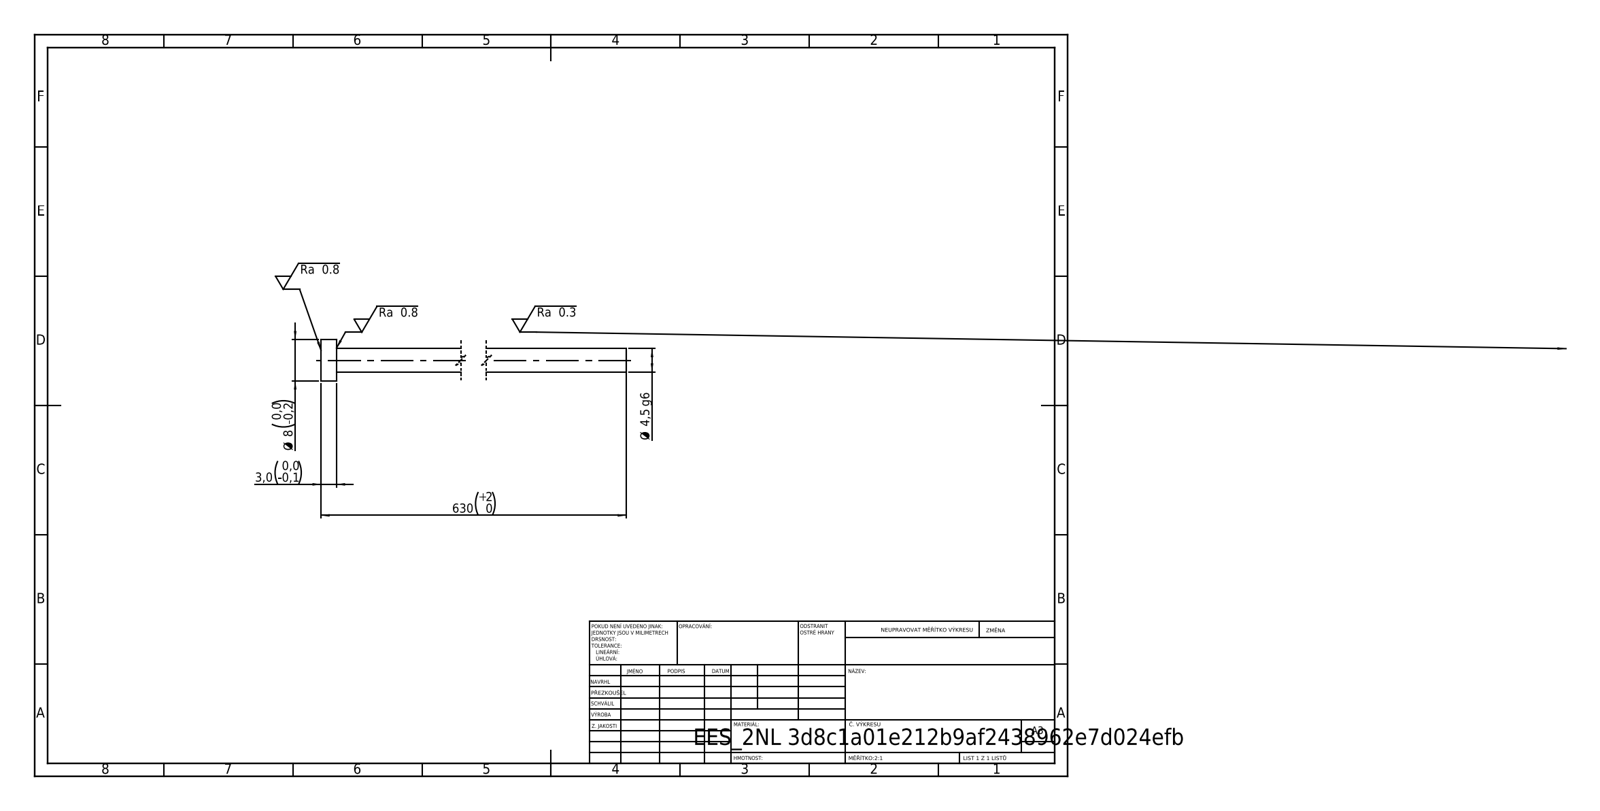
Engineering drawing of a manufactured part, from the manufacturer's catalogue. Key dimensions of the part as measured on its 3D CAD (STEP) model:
STEP written by: SolidWorks 2019 (CONFIG_CONTROL_DESIGN)
Units: millimetres
Bodies: 1 solid, 7 faces (3 planar, 4 cylindrical, 0 other)
Overall size (bounding box): 630 × 8 × 8
Volume: 10 123 mm³ · Surface area: 9 040 mm²
Round bosses / shafts (diameter × count): ⌀8 ×1, ⌀4.5 ×1
Main face-to-face distances: 3, 630, 627
